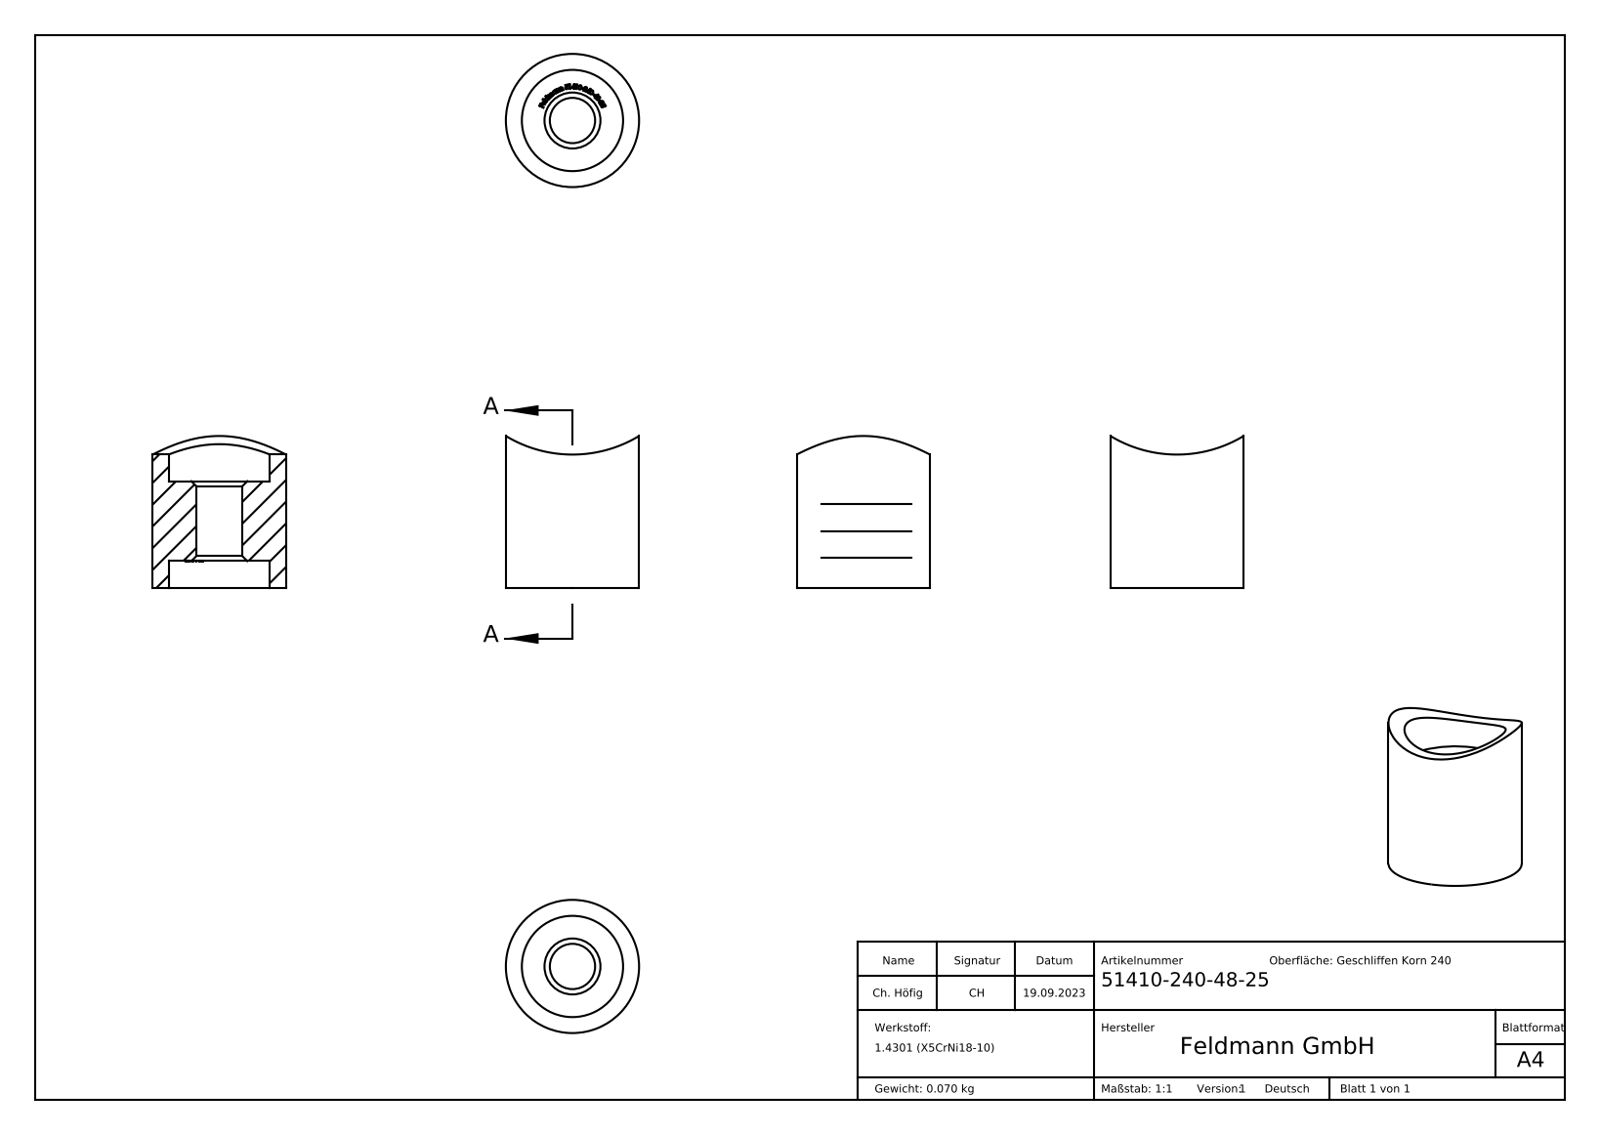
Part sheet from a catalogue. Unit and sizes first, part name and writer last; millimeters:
Units: millimetres
Overall size (bounding box): 28.49 × 25 × 25
Round holes (diameter × count): ⌀8.5 ×1, ⌀19 ×1
Round bosses / shafts (diameter × count): ⌀25 ×1
Partial cylindrical surfaces — rounded edges, fillets, slot ends (radius × count): R24.15 ×1
Main face-to-face distances: 20, 5, 15, 5.1, 14.9, 0.4, 0.43, 0.33, 0.47, 0.36
Volume: 8 835 mm³ · Surface area: 4 012 mm²
Bodies: 1 solid, 295 faces (177 planar, 5 cylindrical, 113 other)
Part name (STEP PRODUCT): 51410-240-48-25
STEP written by: SolidWorks 2018 (CONFIG_CONTROL_DESIGN)
